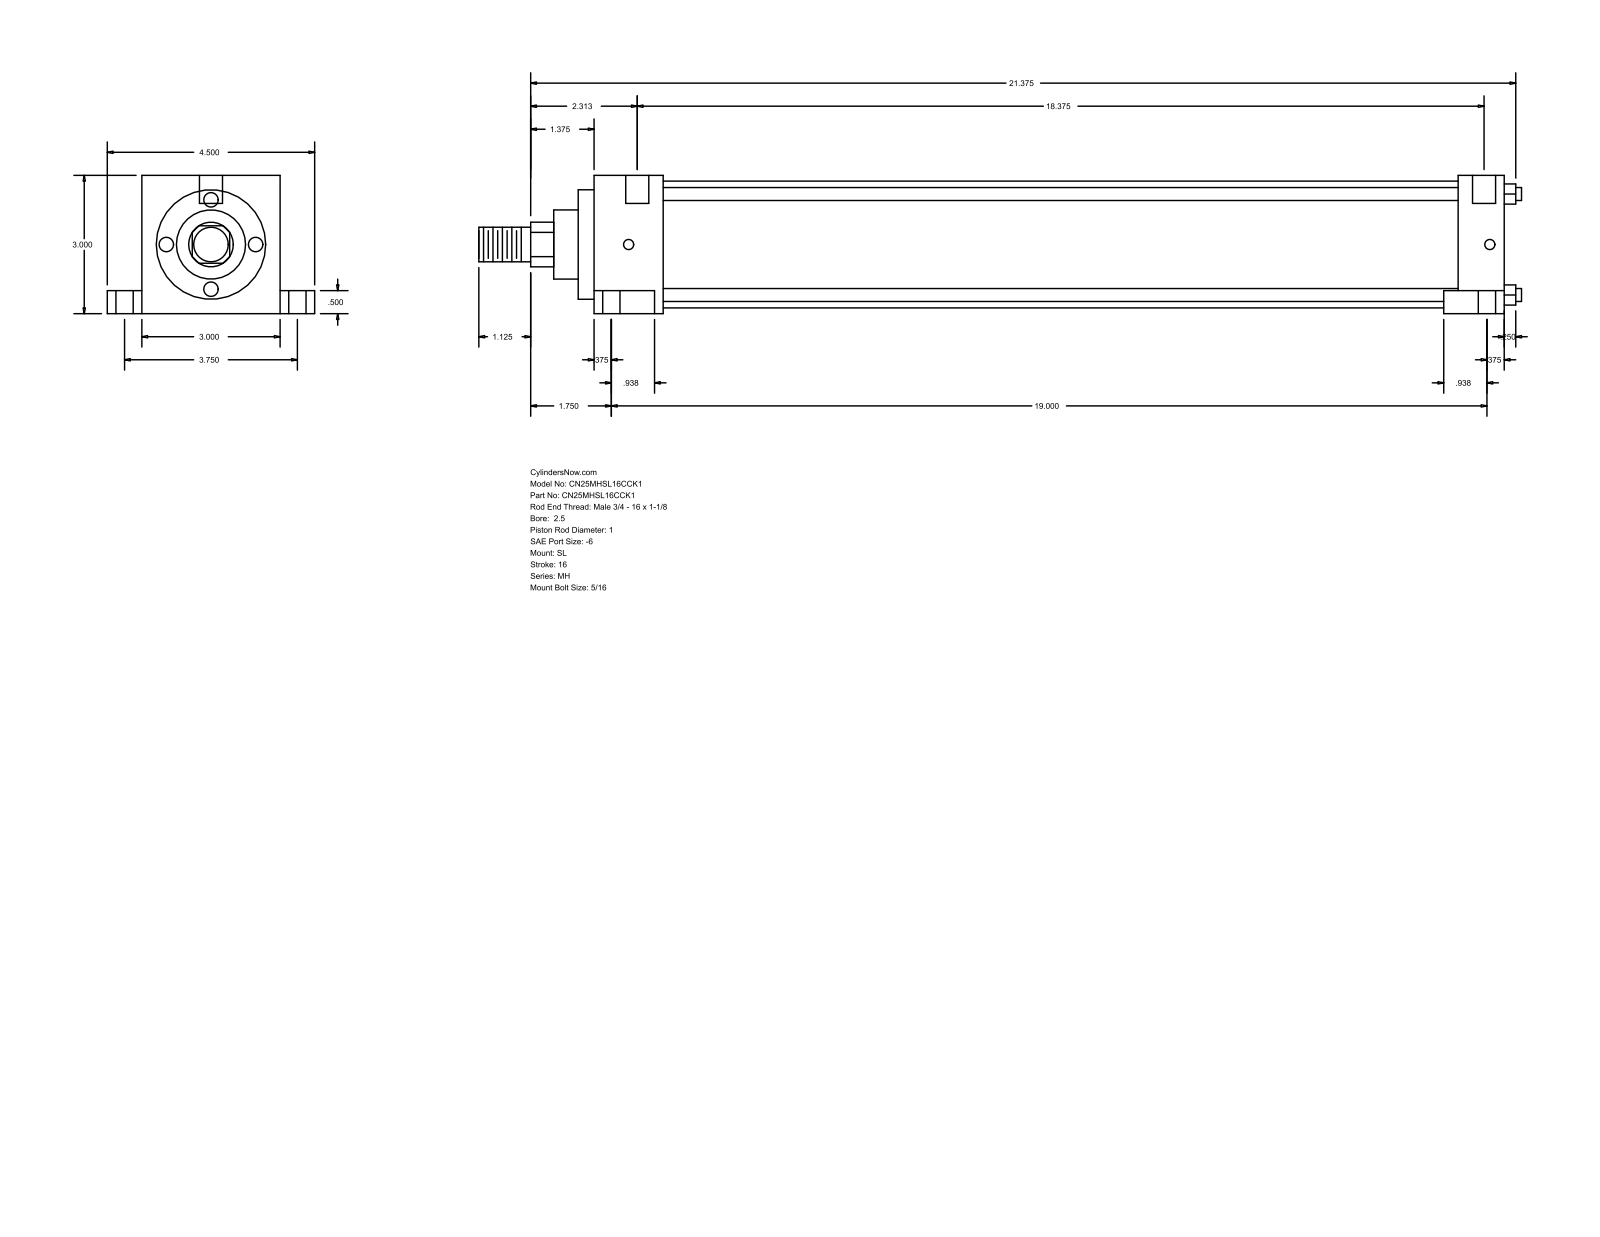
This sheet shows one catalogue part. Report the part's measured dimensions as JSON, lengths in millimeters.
{"part_name": "MH_SL__0250_1", "step_written_by": "GSSL Pune (CONFIG_CONTROL_DESIGN)", "units": "millimeters", "bodies": {"solids": 0, "faces": 86, "planar": 61, "cylindrical": 25, "other": 0}, "overall_size": [574.67, 114.3, 76.2], "round_holes": [[5.56, 2], [9.53, 2], [15.88, 2], [12.7, 1]], "round_bosses_or_shafts": [[7.14, 4], [69.85, 1], [60.33, 1], [38.1, 1], [25.4, 1], [19.05, 1]], "partial_cylinders_radius": [[12.29, 1]], "face_to_face_distances": [76.2, 25.4, 484.99, 510.39, 12.7, 63.5, 19.05, 95.25, 13.49, 498.48], "hole_center_spacings": [47.65, 3.18, 95.24]}
